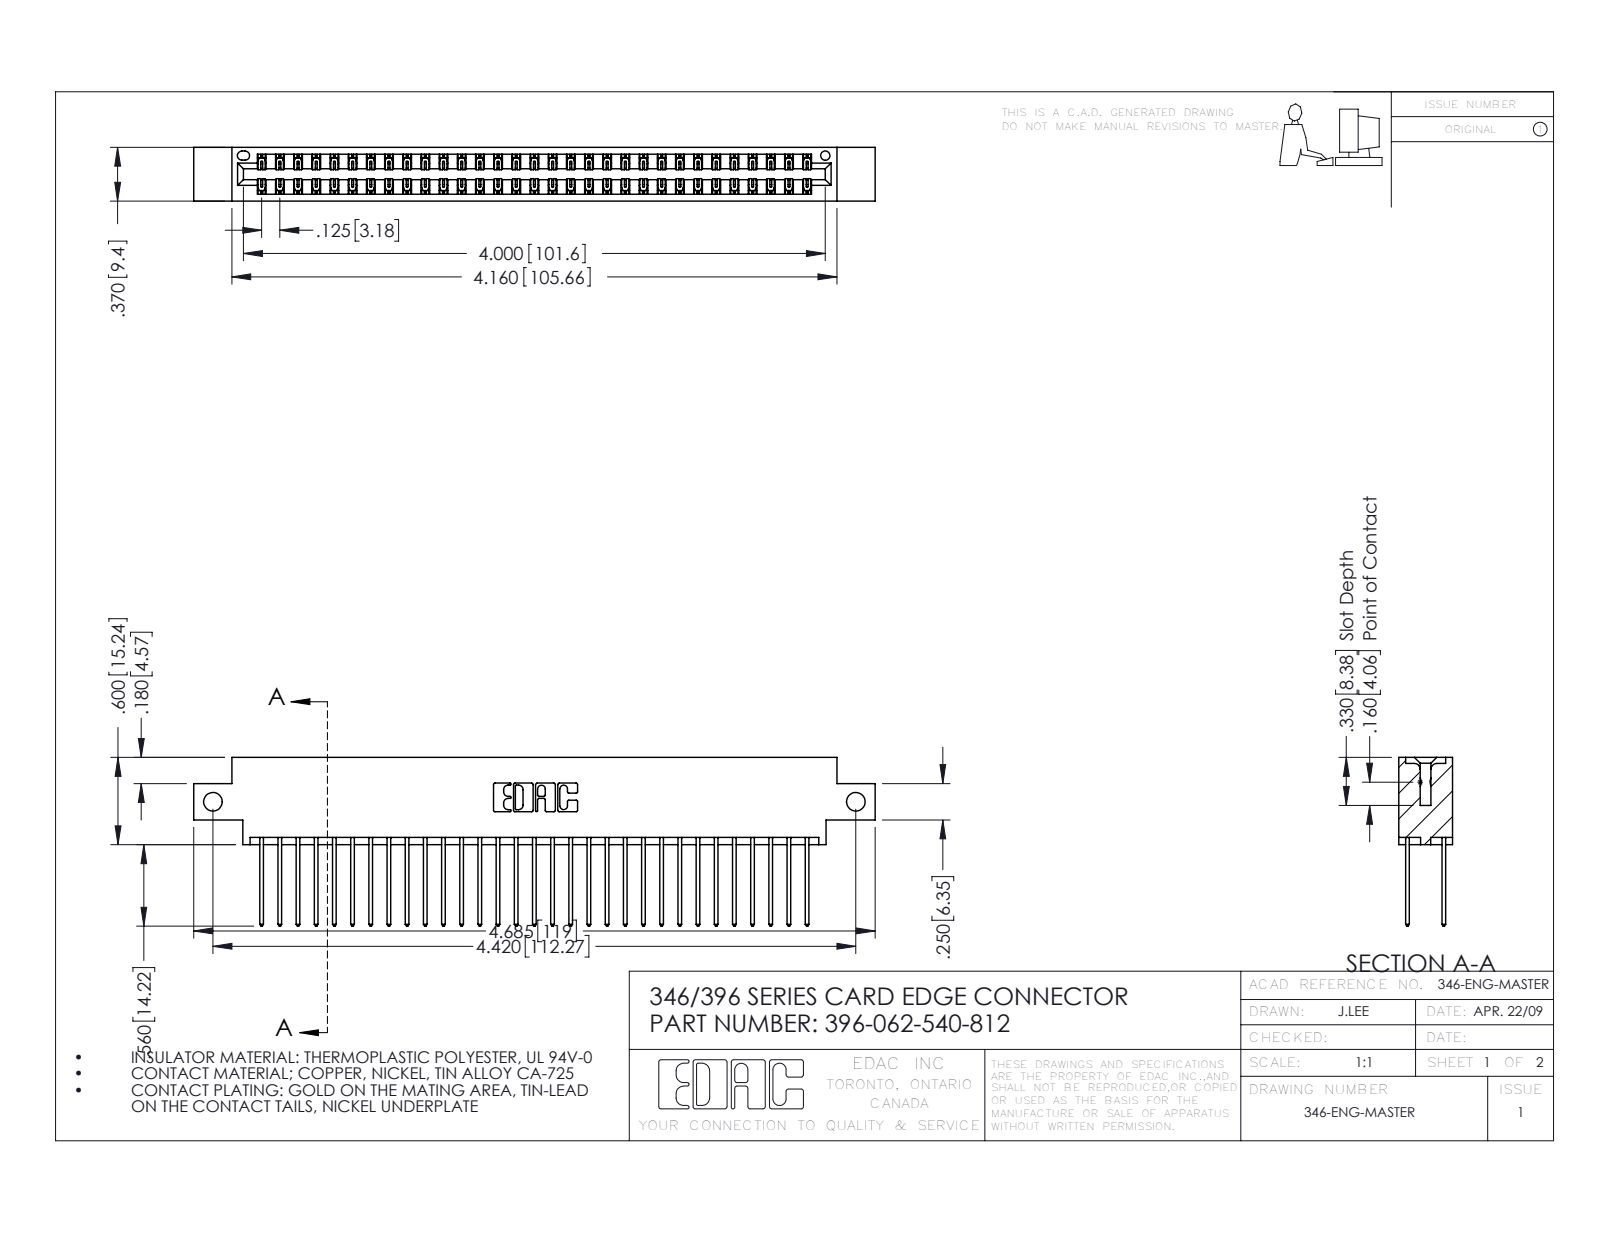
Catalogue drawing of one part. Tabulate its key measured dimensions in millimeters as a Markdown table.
| quantity | value |
| --- | --- |
| part name | 396-062-540-812; 346 Part_0.170 Offset - Side Mount; 345-292-001_345-293-140 |
| STEP written by | SolidWorks 2016 (CONFIG_CONTROL_DESIGN) |
| units | millimeters |
| bodies | 63 solids, 3350 faces (2250 planar, 1100 cylindrical, 0 other) |
| overall size | 119 × 29.5 × 9.4 |
| volume | 11 500 mm³ |
| surface area | 16 810 mm² |
| round holes (diameter × count) | 3.3 × 2, 1.6 × 1 |
| partial cylindrical surfaces (radius × count) | 0.2 × 93, 0.3 × 62, 0.3 × 22, 0.2 × 6, 0.8 × 6, 0.7 × 3, 0.4 × 2, 0.6 × 2 |
| main face-to-face distances | 1.2, 8.2, 6.4, 9.4, 1.8, 7.6, 0.6, 7, 3.8, 5.6 |
| hole center spacings | 112.3 |
